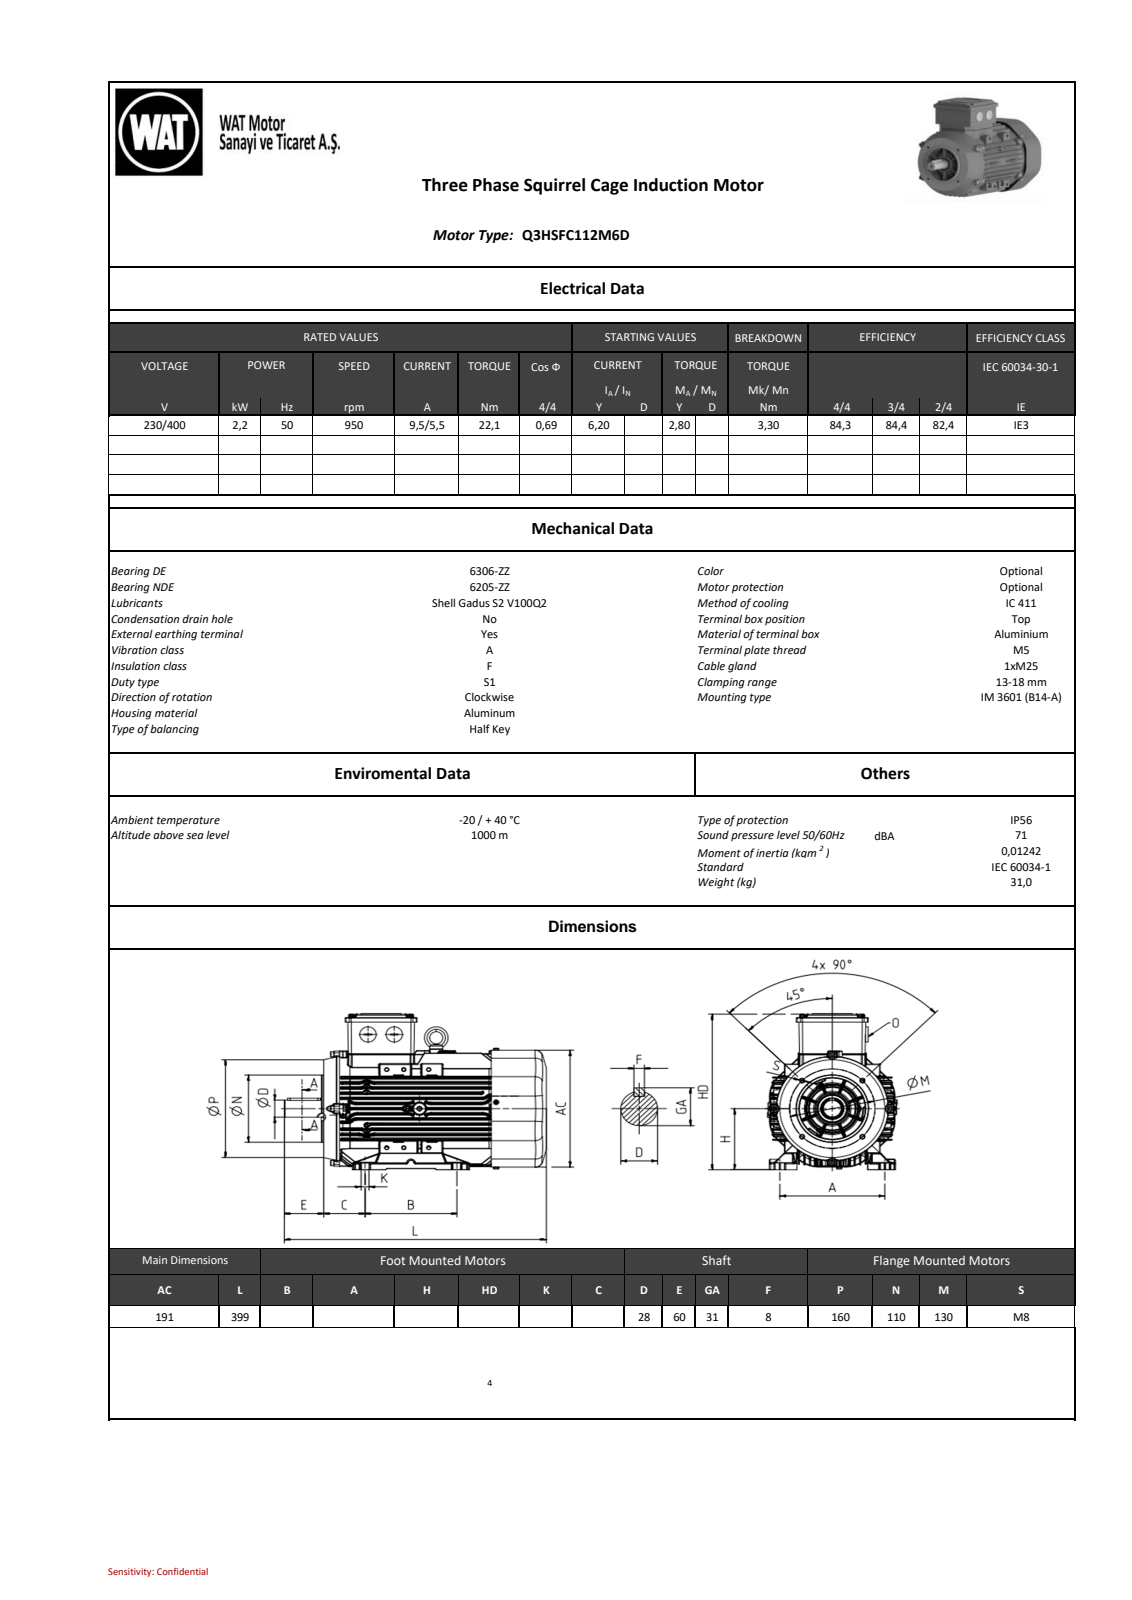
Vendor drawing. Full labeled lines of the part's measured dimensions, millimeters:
Part name (STEP PRODUCT): QHS Series_ 112_B14a_stp_objects
STEP written by: SIEMENS PLM Software NX2206.8101 (AUTOMOTIVE_DESIGN)
Units: millimetres
Bodies: 0 solids, 5501 faces (1221 planar, 2172 cylindrical, 2108 other)
Overall size (bounding box): 399.31 × 242.09 × 197.75
Round holes (diameter × count): ⌀6.8 ×4, ⌀10 ×1, ⌀44.42 ×1, ⌀57.4 ×1, ⌀89 ×1, ⌀109 ×1, ⌀129 ×1, ⌀133 ×1
Round bosses / shafts (diameter × count): ⌀8 ×8, ⌀8.5 ×4, ⌀5 ×4, ⌀25 ×3, ⌀113.5 ×1, ⌀110 ×1, ⌀93.5 ×1, ⌀60.74 ×1
Partial cylindrical surfaces — rounded edges, fillets, slot ends (radius × count): R0.8 ×670, R1 ×495, R2 ×89, R0.5 ×79, R0.81 ×51, R5 ×40, R15 ×26, R45 ×16
Main face-to-face distances: 8.53, 8.46, 8.45, 76.24, 16.91, 93.45, 25.58, 17.05, 76.68, 59.63
Hole centre spacings: 65, 91.92, 129.99
